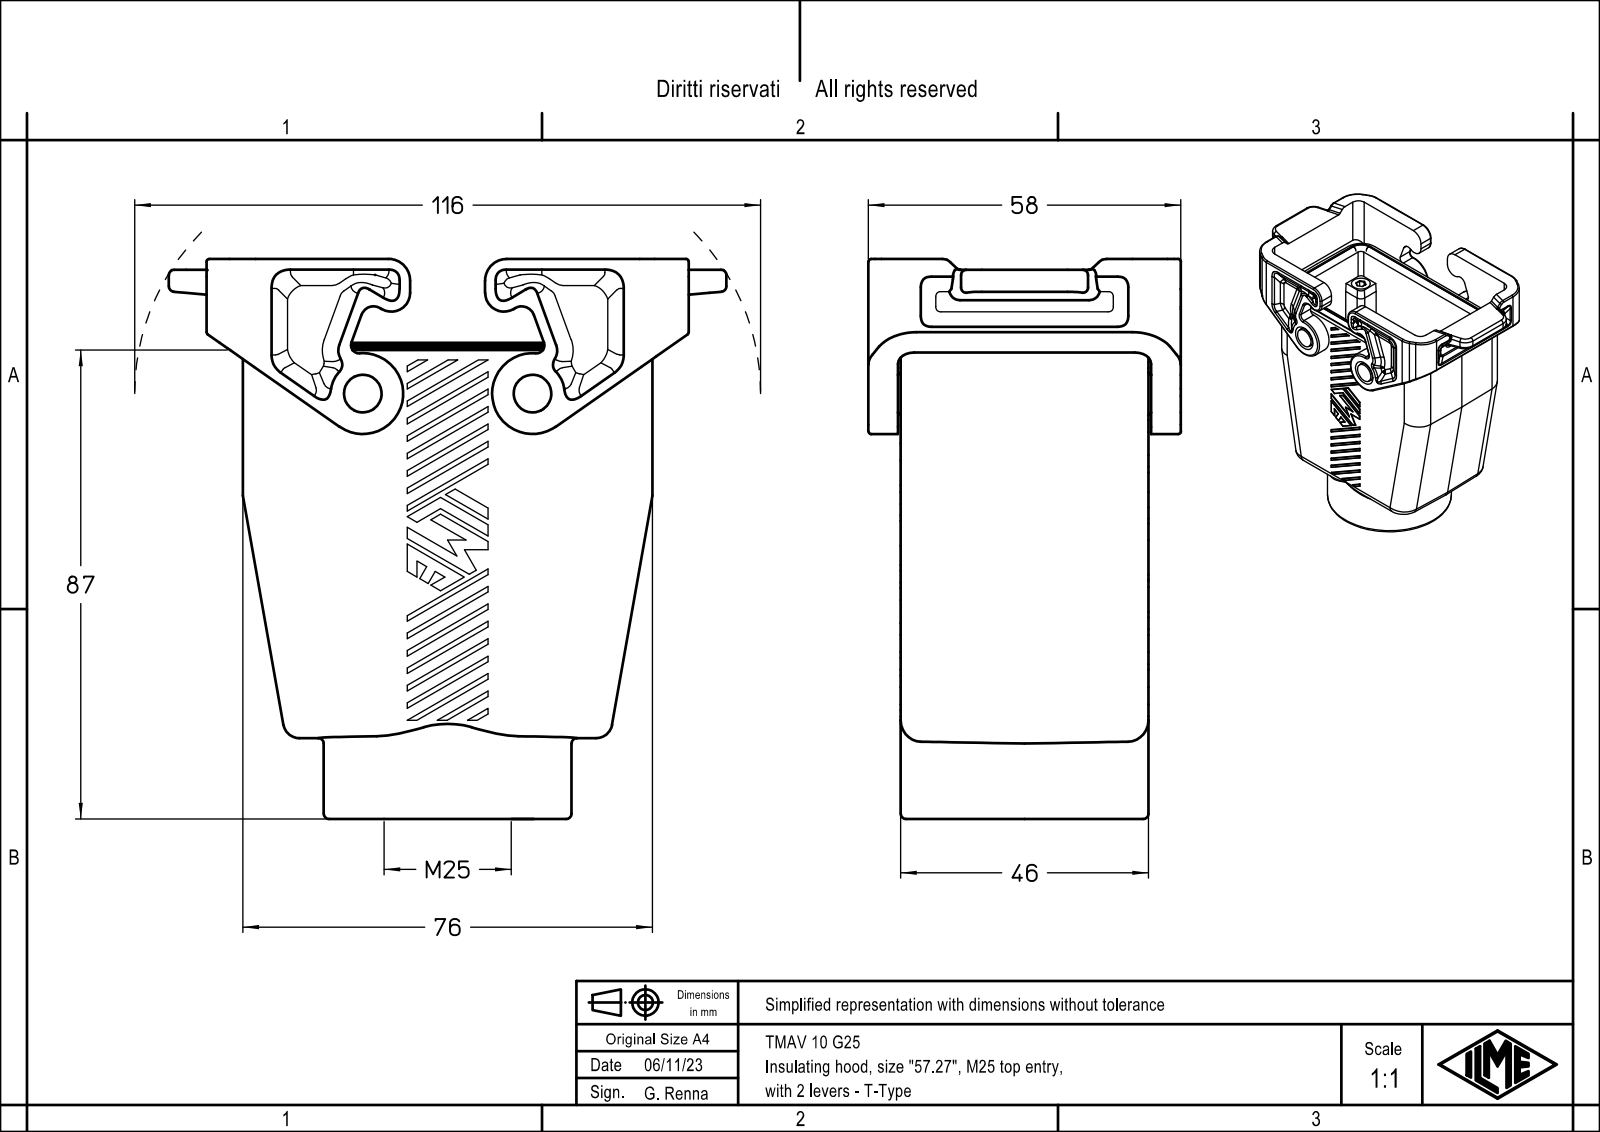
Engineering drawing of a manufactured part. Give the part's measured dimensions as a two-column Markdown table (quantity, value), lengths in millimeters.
| quantity | value |
| --- | --- |
| part name | TMAV 10 G25 |
| STEP written by | Creo Elements/Direct Modeling 20.1B 02-Apr-2019 (C) Parametric Technology GmbH (AUTOMOTIVE_DESIGN) |
| units | millimeters |
| bodies | 1 solid, 664 faces (240 planar, 362 cylindrical, 62 other) |
| overall size | 103.9 × 103.5 × 58 |
| volume | 139 612 mm³ |
| surface area | 51 132 mm² |
| round holes (diameter × count) | 21 × 1, 23.6 × 1 |
| round bosses / shafts (diameter × count) | 7 × 2, 46 × 1 |
| partial cylindrical surfaces (radius × count) | 0.15 × 128, 3 × 20, 1 × 16, 2 × 16, 1.5 × 10, 1.3 × 8, 6 × 8, 7 × 8 |
| main face-to-face distances | 5.4, 40.6, 46, 35.2, 0.5, 5.9, 41.1, 46.5, 5.5, 52.5 |
